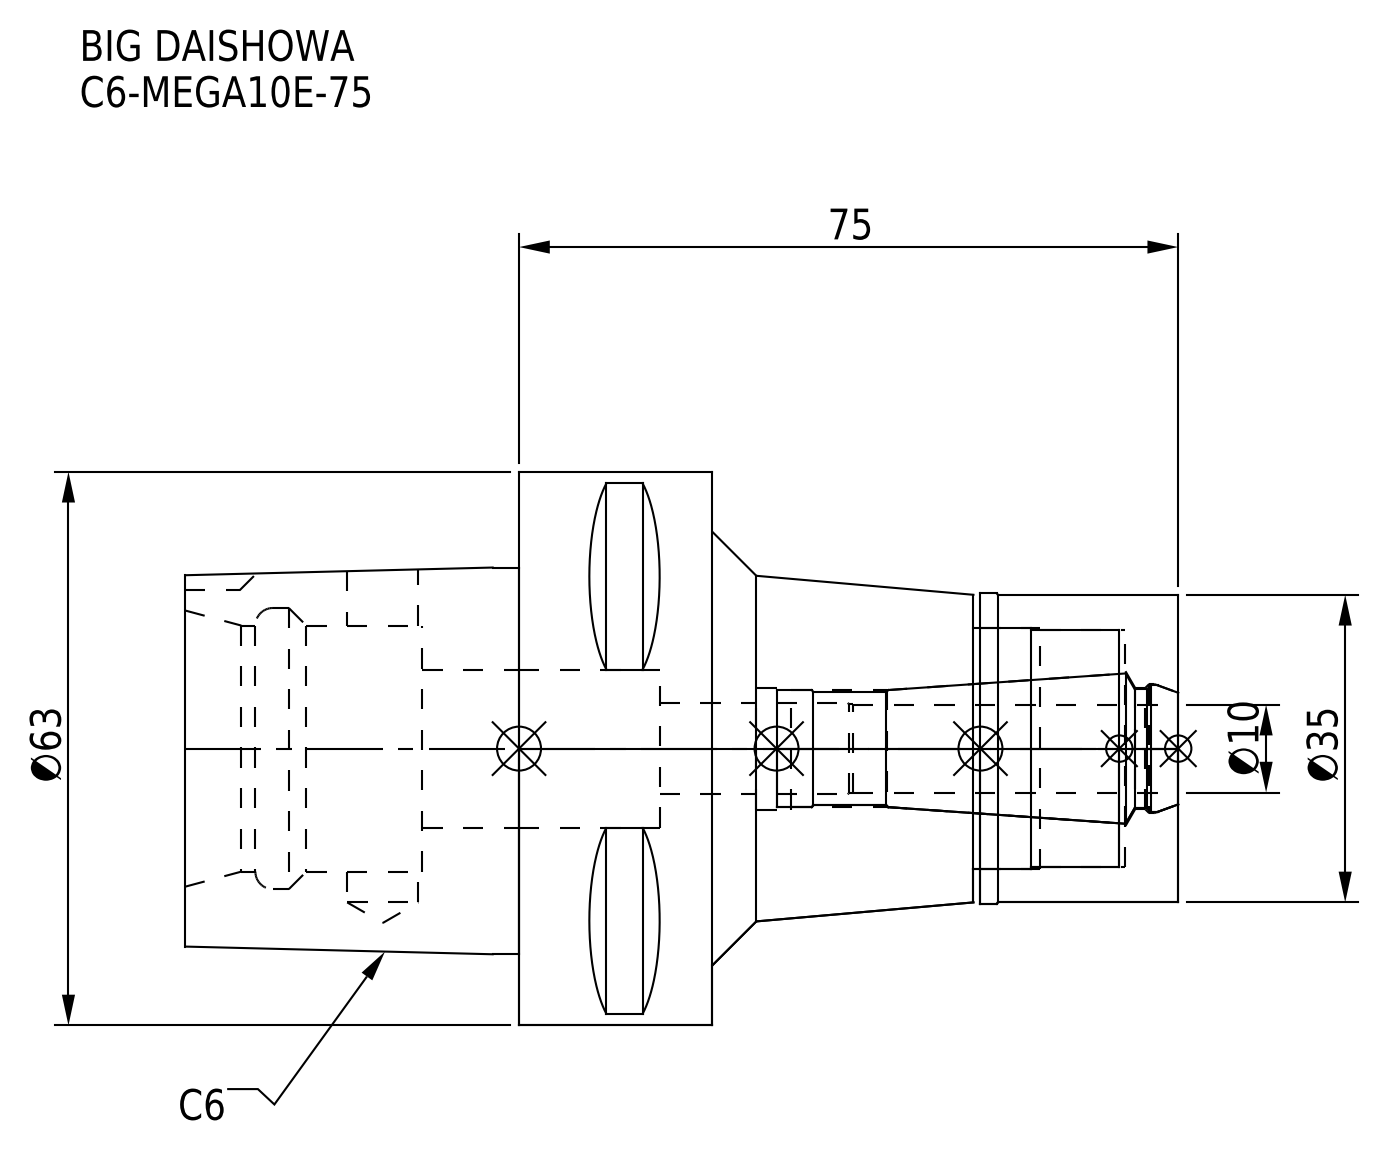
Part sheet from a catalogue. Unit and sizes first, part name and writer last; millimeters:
Units: millimetres
Overall size (bounding box): 113 × 63 × 63
Round holes (diameter × count): ⌀8.1 ×1, ⌀10.4 ×1, ⌀13.3 ×1, ⌀13.8 ×1, ⌀13.9 ×1, ⌀14.7 ×1, ⌀18 ×1, ⌀27 ×1, ⌀27.5 ×1, ⌀28 ×1, ⌀32 ×1
Round bosses / shafts (diameter × count): ⌀63 ×1, ⌀35.3 ×1, ⌀35 ×1
Partial cylindrical surfaces — rounded edges, fillets, slot ends (radius × count): R5 ×1
Main face-to-face distances: 22, 53, 75, 27, 38, 6, 113, 60, 11, 22.5
Volume: 144 068 mm³ · Surface area: 32 312 mm²
Bodies: 2 solids, 97 faces (36 planar, 37 cylindrical, 24 other)
Part name (STEP PRODUCT): C6-MEGA10E-75-100_ASM.stp; C6-MEGA10E-75-100.stp; C6-MEGA10E-75_1.stp; C6-MEGA10E-75 (+3 more)
STEP written by: SolidWorks 2019 (CONFIG_CONTROL_DESIGN)
